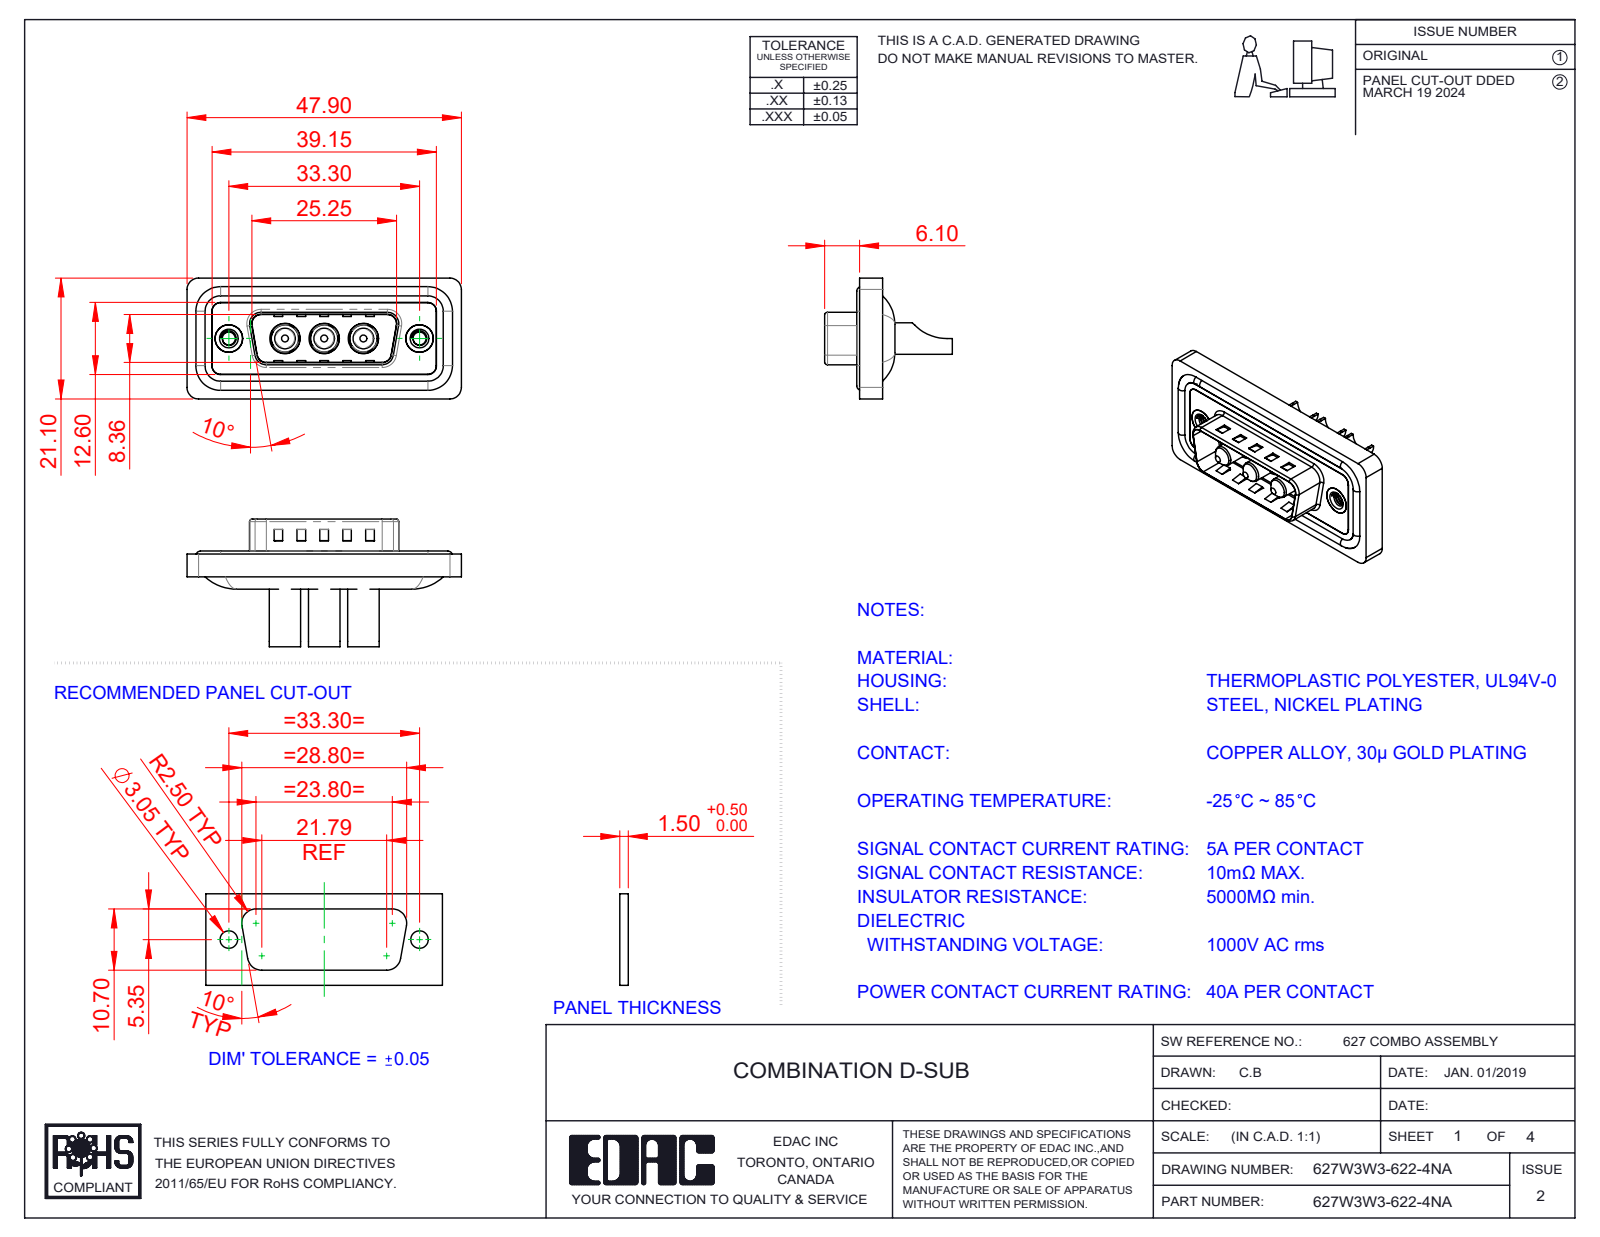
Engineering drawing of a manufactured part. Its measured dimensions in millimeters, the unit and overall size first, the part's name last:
Units: millimetres
Overall size (bounding box): 47.9 × 22.3 × 21.1
Round holes (diameter × count): ⌀4.6 ×3, ⌀4.85 ×3, ⌀5.3 ×3, ⌀2.26 ×2, ⌀4 ×2, ⌀4.8 ×2, ⌀5 ×2
Round bosses / shafts (diameter × count): ⌀1.6 ×4, ⌀5.5 ×3, ⌀5.2 ×3, ⌀4.75 ×3, ⌀3.75 ×3, ⌀3.6 ×3, ⌀4.9 ×2
Partial cylindrical surfaces — rounded edges, fillets, slot ends (radius × count): R1.5 ×26, R2 ×20, R0.5 ×8, R1.6 ×8, R0.25 ×4, R0.6 ×4, R0.65 ×4, R0.9 ×4
Main face-to-face distances: 0.4, 1.1, 0.5, 1.6, 3.1, 2.9, 1.5, 0.82, 9.58, 2.5
Hole centre spacings: 6.85, 9.8, 16.65, 23.5, 13.7, 33.3
Volume: 5 707 mm³ · Surface area: 9 171 mm²
Bodies: 13 solids, 574 faces (213 planar, 246 cylindrical, 115 other)
Part name (STEP PRODUCT): 627Combo Threaded Rivet_A; 627Combo Housing_3W3; 627W3W3-622-4NA; Power Pin_40A SC (+3 more)
STEP written by: SolidWorks 2023 (CONFIG_CONTROL_DESIGN)
